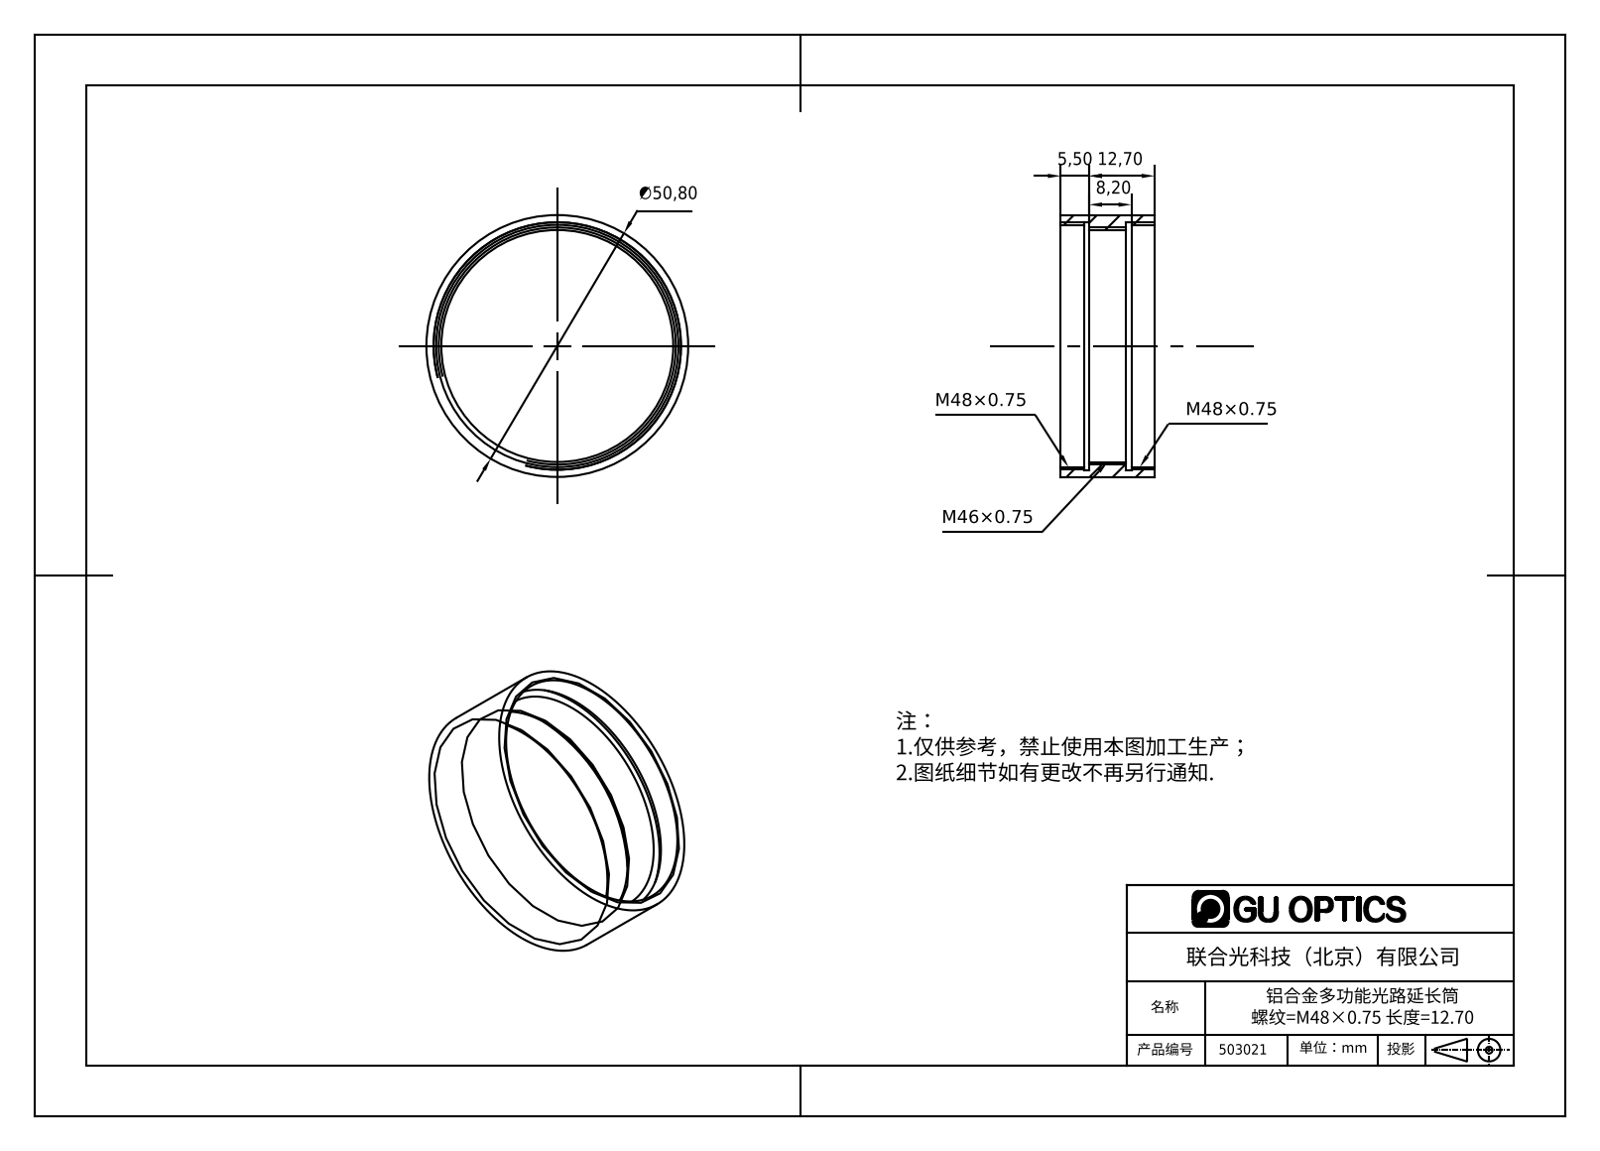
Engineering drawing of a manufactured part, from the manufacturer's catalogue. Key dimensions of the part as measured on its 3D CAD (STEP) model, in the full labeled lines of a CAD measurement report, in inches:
Part name (STEP PRODUCT): 503021
STEP written by: SolidWorks 2016 (AUTOMOTIVE_DESIGN)
Units: inches
Bodies: 1 solid, 18 faces (6 planar, 12 cylindrical, 0 other)
Overall size (bounding box): 2 × 2 × 0.717
Volume: 0.377 in³ · Surface area: 10.52 in²
Round holes (diameter × count): ⌀1.772 ×1, ⌀1.85 ×1, ⌀1.898 ×1
Round bosses / shafts (diameter × count): ⌀2 ×1
Main face-to-face distances: 0.217, 0.5, 0.717, 0.283, 0.177, 0.539, 0.039, 0.323, 0.362
